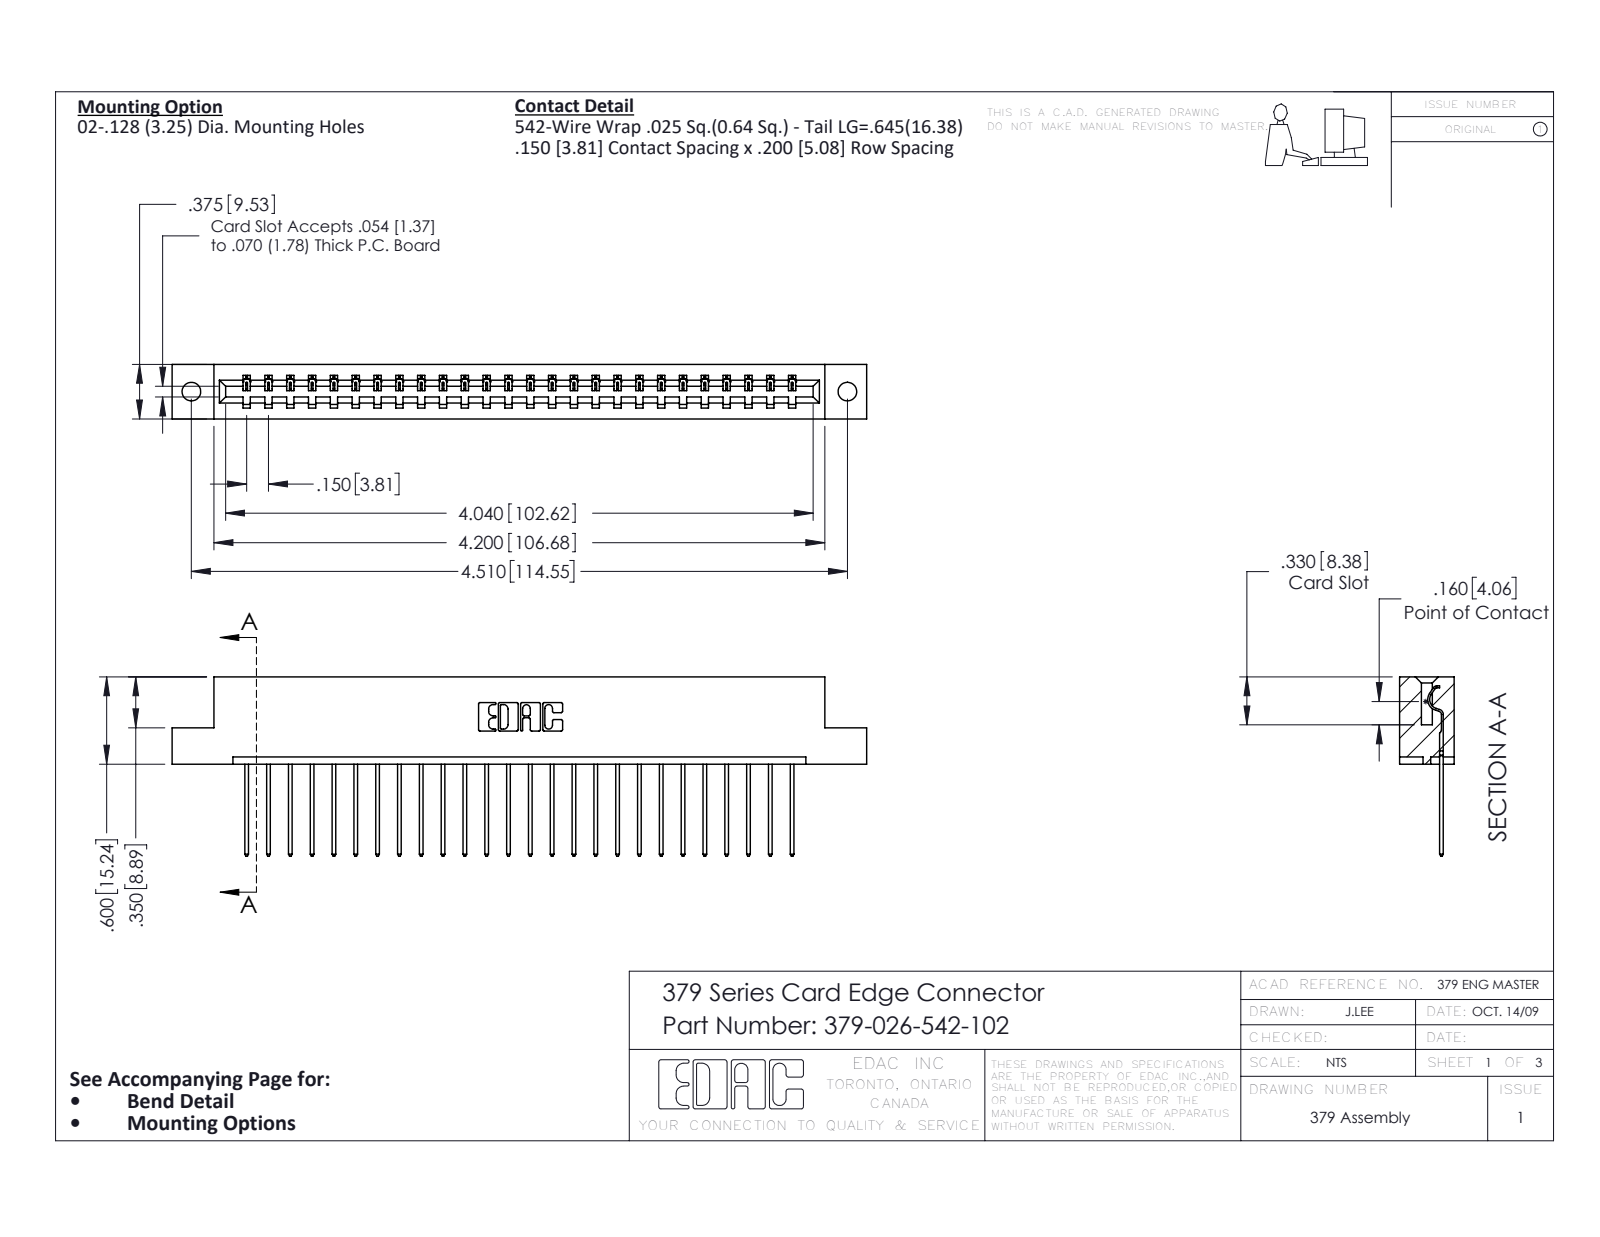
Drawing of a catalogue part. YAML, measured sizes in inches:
part_name: "379-026-542-102; 345-292-001_345-293-142; 379 Part_Flush - .128 Dia"
step_written_by: "SolidWorks 2016 (CONFIG_CONTROL_DESIGN)"
units: inches
bodies: {solids: 27, faces: 1622, planar: 1162, cylindrical: 460, other: 0}
overall_size: [4.775, 1.232, 0.375]
volume: 0.767
surface_area: 19.99
round_holes:
  - {diameter: 0.128, count: 2}
partial_cylinders:
  - {radius: 0.006, count: 52}
  - {radius: 0.01, count: 52}
  - {radius: 0.01, count: 22}
  - {radius: 0.007, count: 6}
  - {radius: 0.031, count: 6}
  - {radius: 0.026, count: 3}
  - {radius: 0.014, count: 1}
  - {radius: 0.022, count: 1}
face_to_face_distances: [0.3, 0.075, 0.375, 0.225, 0.6, 0.275, 0.1, 0.025, 0.2, 0.15]
hole_center_spacings: [4.51]
